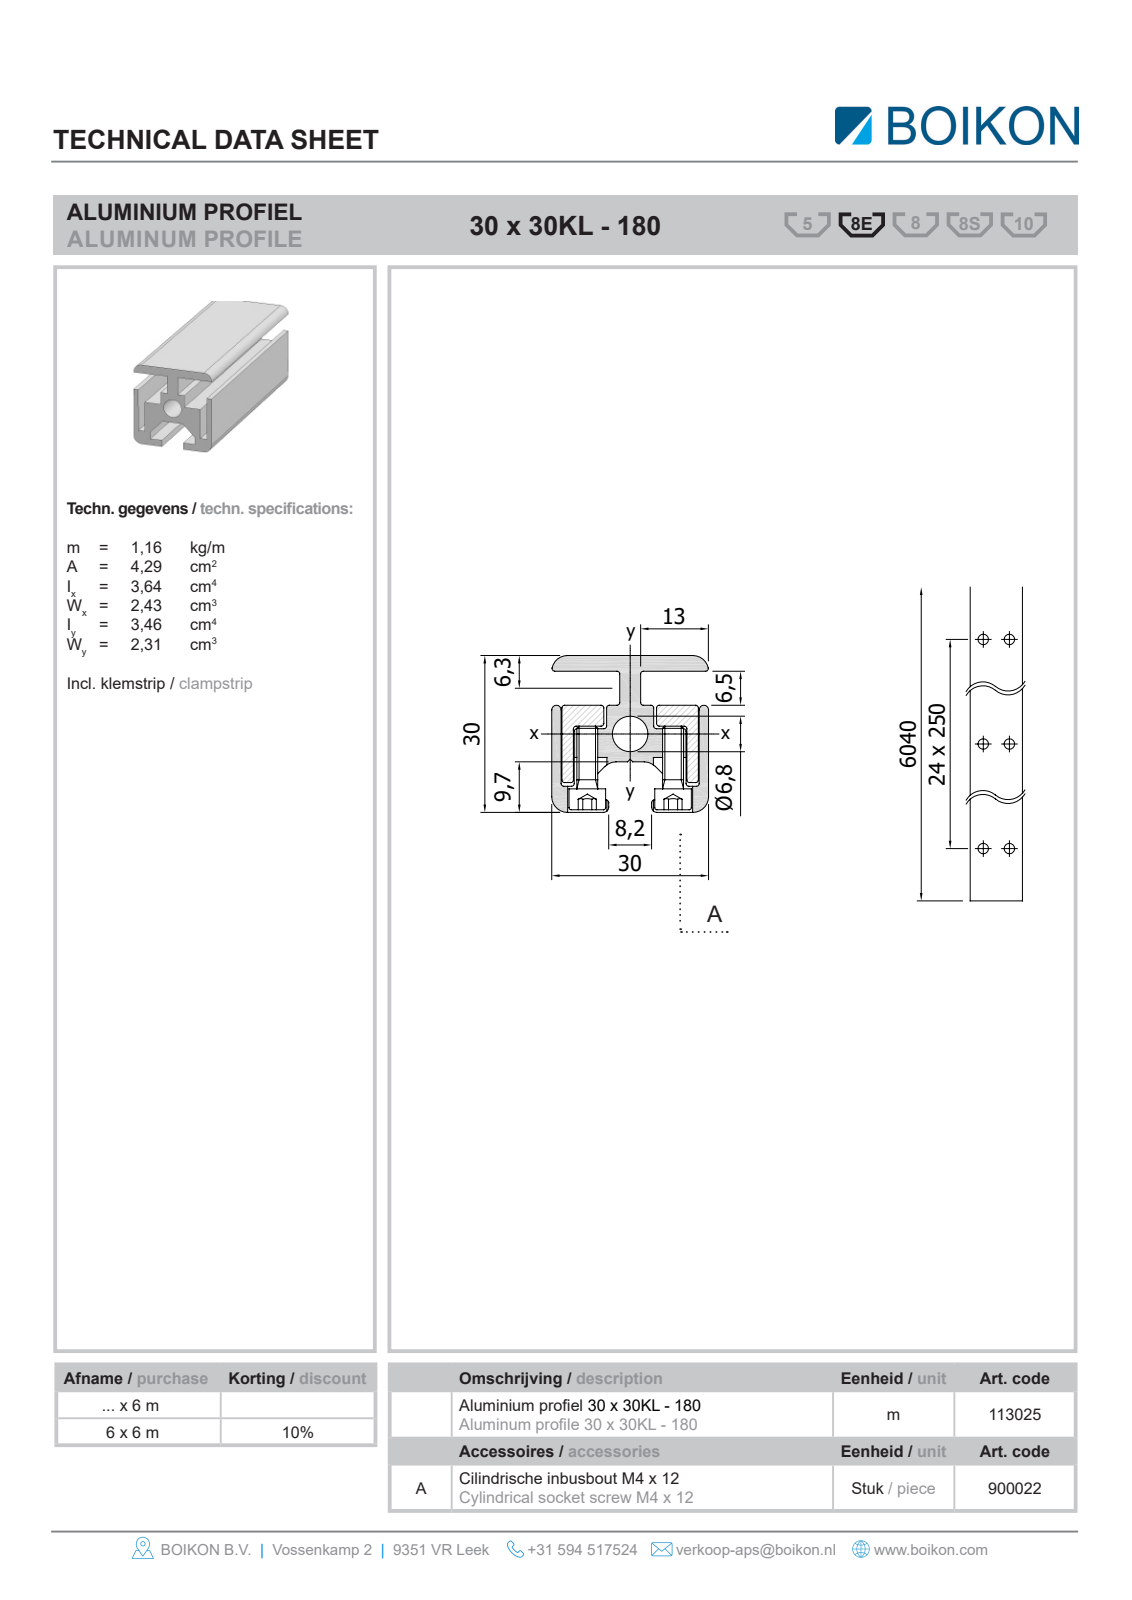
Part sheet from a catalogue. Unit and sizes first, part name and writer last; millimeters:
Units: millimetres
Overall size (bounding box): 1000 × 30 × 30
Round holes (diameter × count): ⌀6.8 ×1
Partial cylindrical surfaces — rounded edges, fillets, slot ends (radius × count): R3 ×4
Main face-to-face distances: 30, 2.5, 1.8, 28.2, 3, 4.3, 25.7, 8.7, 15.2, 23.9
Volume: 430 641 mm³ · Surface area: 282 951 mm²
Bodies: 1 solid, 39 faces (34 planar, 5 cylindrical, 0 other)
Part name (STEP PRODUCT): Root; 11302530x30-KL180BOIKON0
STEP written by: HiCAD 2013 1802.4 Build 509 (AUTOMOTIVE_DESIGN)
